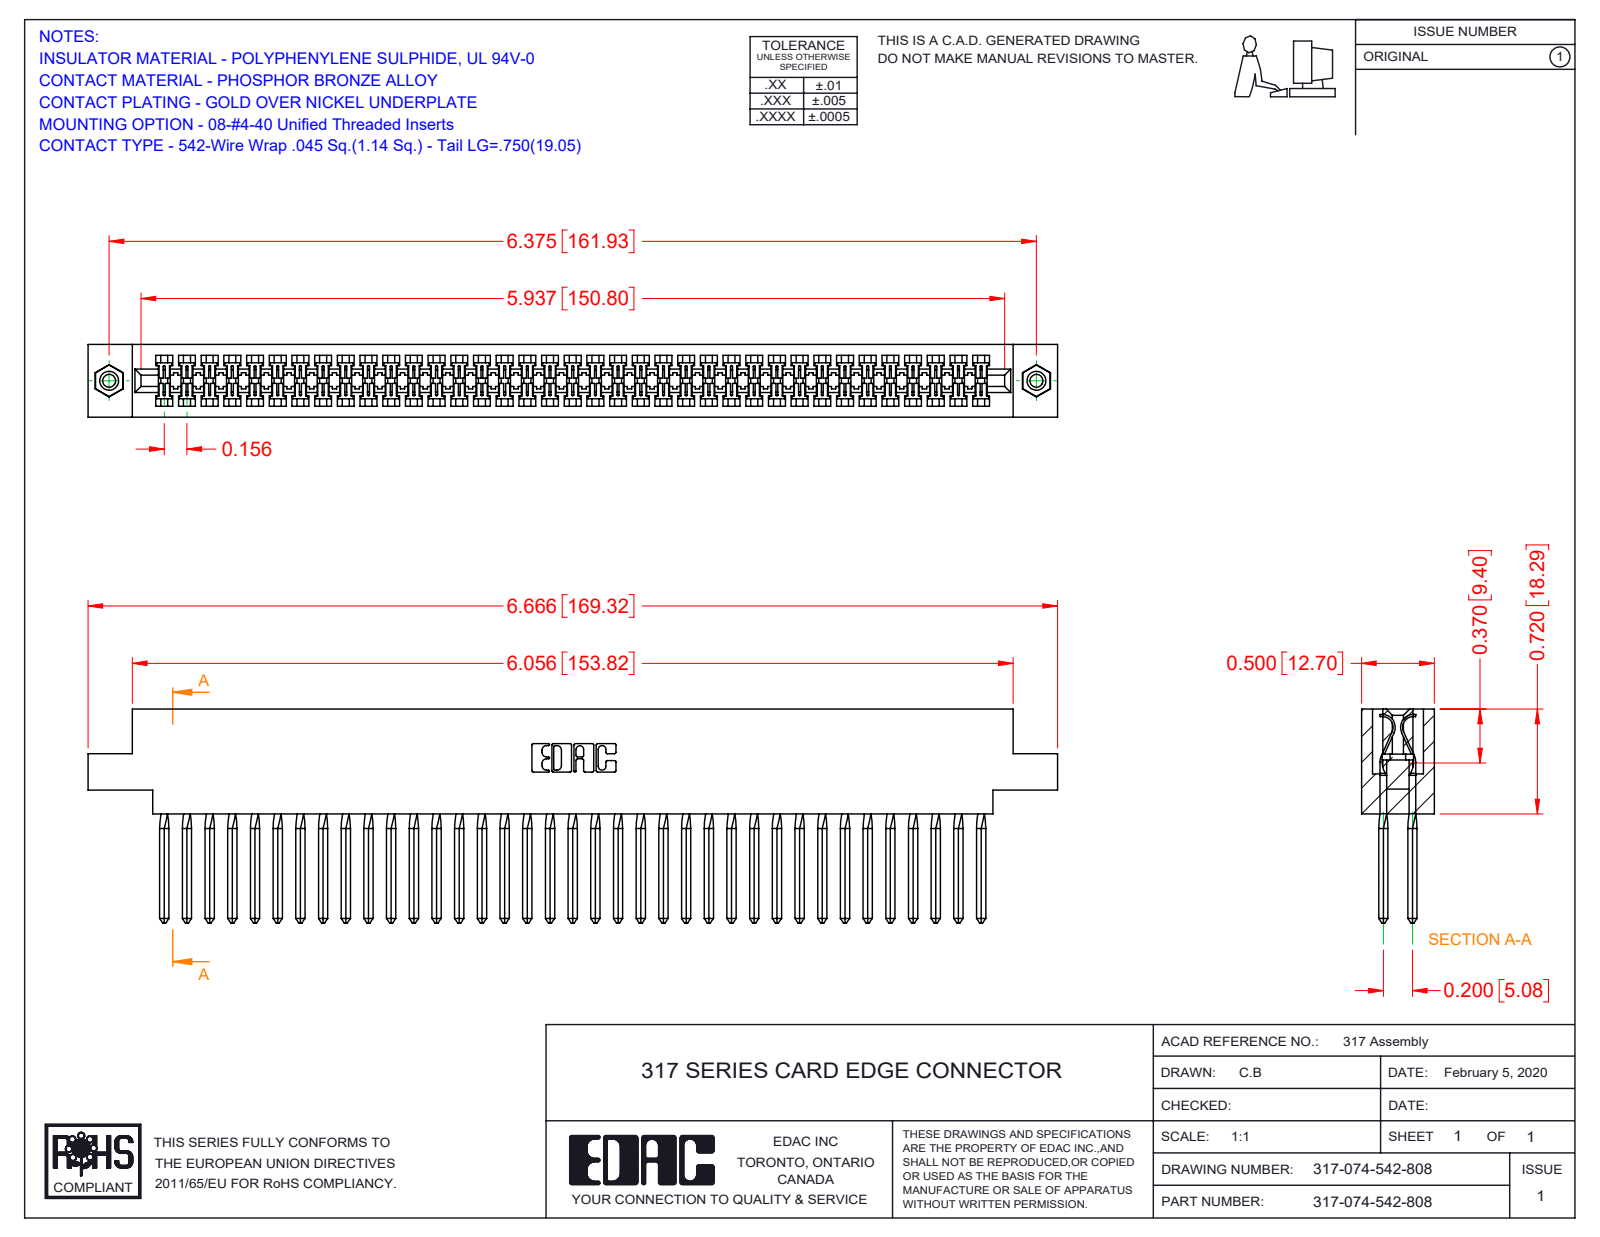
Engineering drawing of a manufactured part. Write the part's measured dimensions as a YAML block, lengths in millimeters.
part_name: "317-074-542-808; 317-290-003_542; 345-250-001_345-250-003-102; 317 Part_.156 Dia - TI"
step_written_by: "SolidWorks 2016 (CONFIG_CONTROL_DESIGN)"
units: millimeters
bodies: {solids: 77, faces: 4380, planar: 3494, cylindrical: 574, other: 312}
overall_size: [169.3, 37.3, 12.7]
volume: 27560
surface_area: 38190
round_holes:
  - {diameter: 2.3, count: 2}
  - {diameter: 3.2, count: 2}
  - {diameter: 4, count: 2}
round_bosses_or_shafts:
  - {diameter: 3.9, count: 2}
partial_cylinders:
  - {radius: 0.2, count: 148}
  - {radius: 0.3, count: 22}
  - {radius: 0.2, count: 6}
  - {radius: 0.8, count: 6}
  - {radius: 0.7, count: 3}
  - {radius: 1.9, count: 2}
  - {radius: 2.3, count: 2}
  - {radius: 2.5, count: 2}
face_to_face_distances: [12.7, 1.9, 10.8, 8.9, 5.1, 1.2, 3.3, 9.4, 1.3, 7.5]
hole_center_spacings: [161.9]
